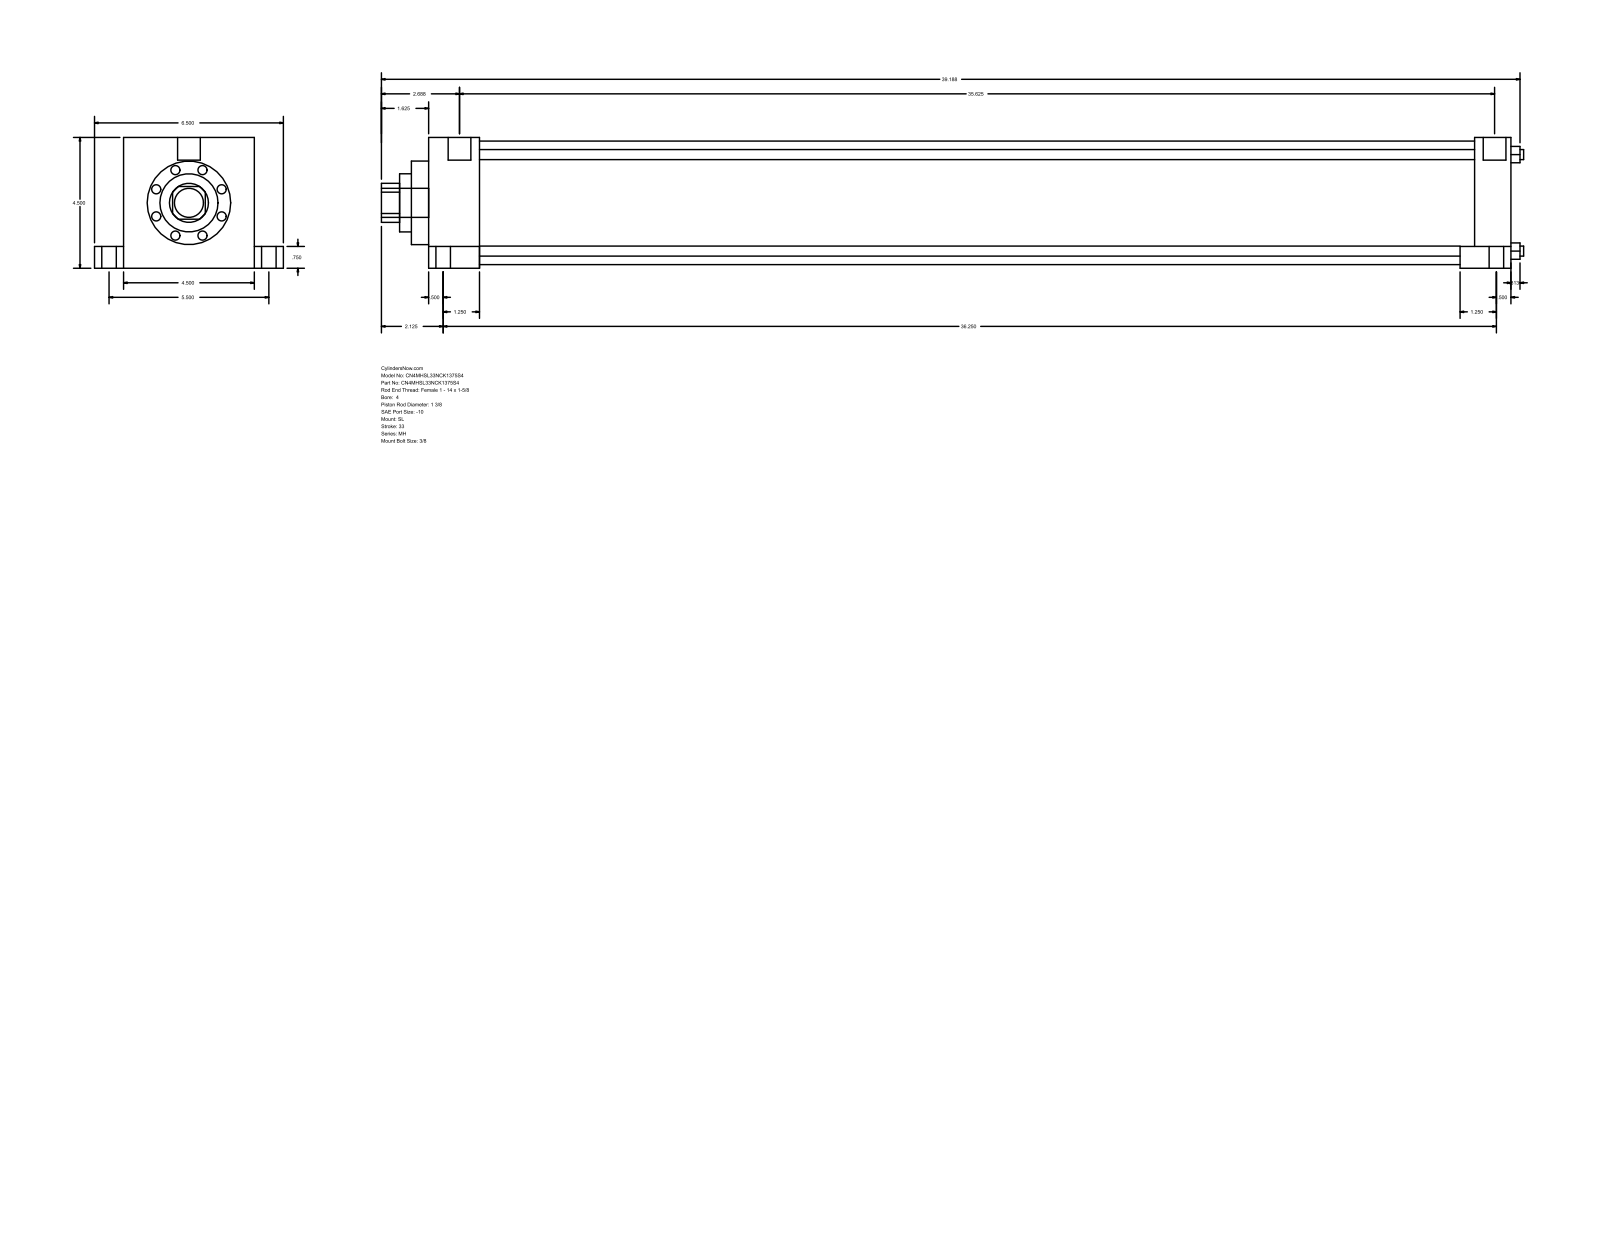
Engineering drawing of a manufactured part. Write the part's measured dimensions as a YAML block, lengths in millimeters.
part_name: "MH_SL__0400_1.375"
step_written_by: "GSSL Pune (CONFIG_CONTROL_DESIGN)"
units: millimeters
bodies: {solids: 0, faces: 110, planar: 77, cylindrical: 33, other: 0}
overall_size: [998.54, 165.1, 114.3]
round_holes:
  - {diameter: 8.76, count: 4}
  - {diameter: 34.92, count: 1}
  - {diameter: 50.8, count: 1}
  - {diameter: 73.03, count: 1}
  - {diameter: 107.95, count: 1}
round_bosses_or_shafts:
  - {diameter: 19.05, count: 4}
  - {diameter: 12.7, count: 4}
  - {diameter: 8.73, count: 4}
  - {diameter: 19.84, count: 2}
  - {diameter: 25.4, count: 1}
partial_cylinders:
  - {radius: 17.06, count: 1}
face_to_face_distances: [114.3, 946.15, 44.45, 901.7, 914.4, 869.95, 31.75, 25.4, 139.7, 19.05]
hole_center_spacings: [59.62, 84.32, 119.25]
